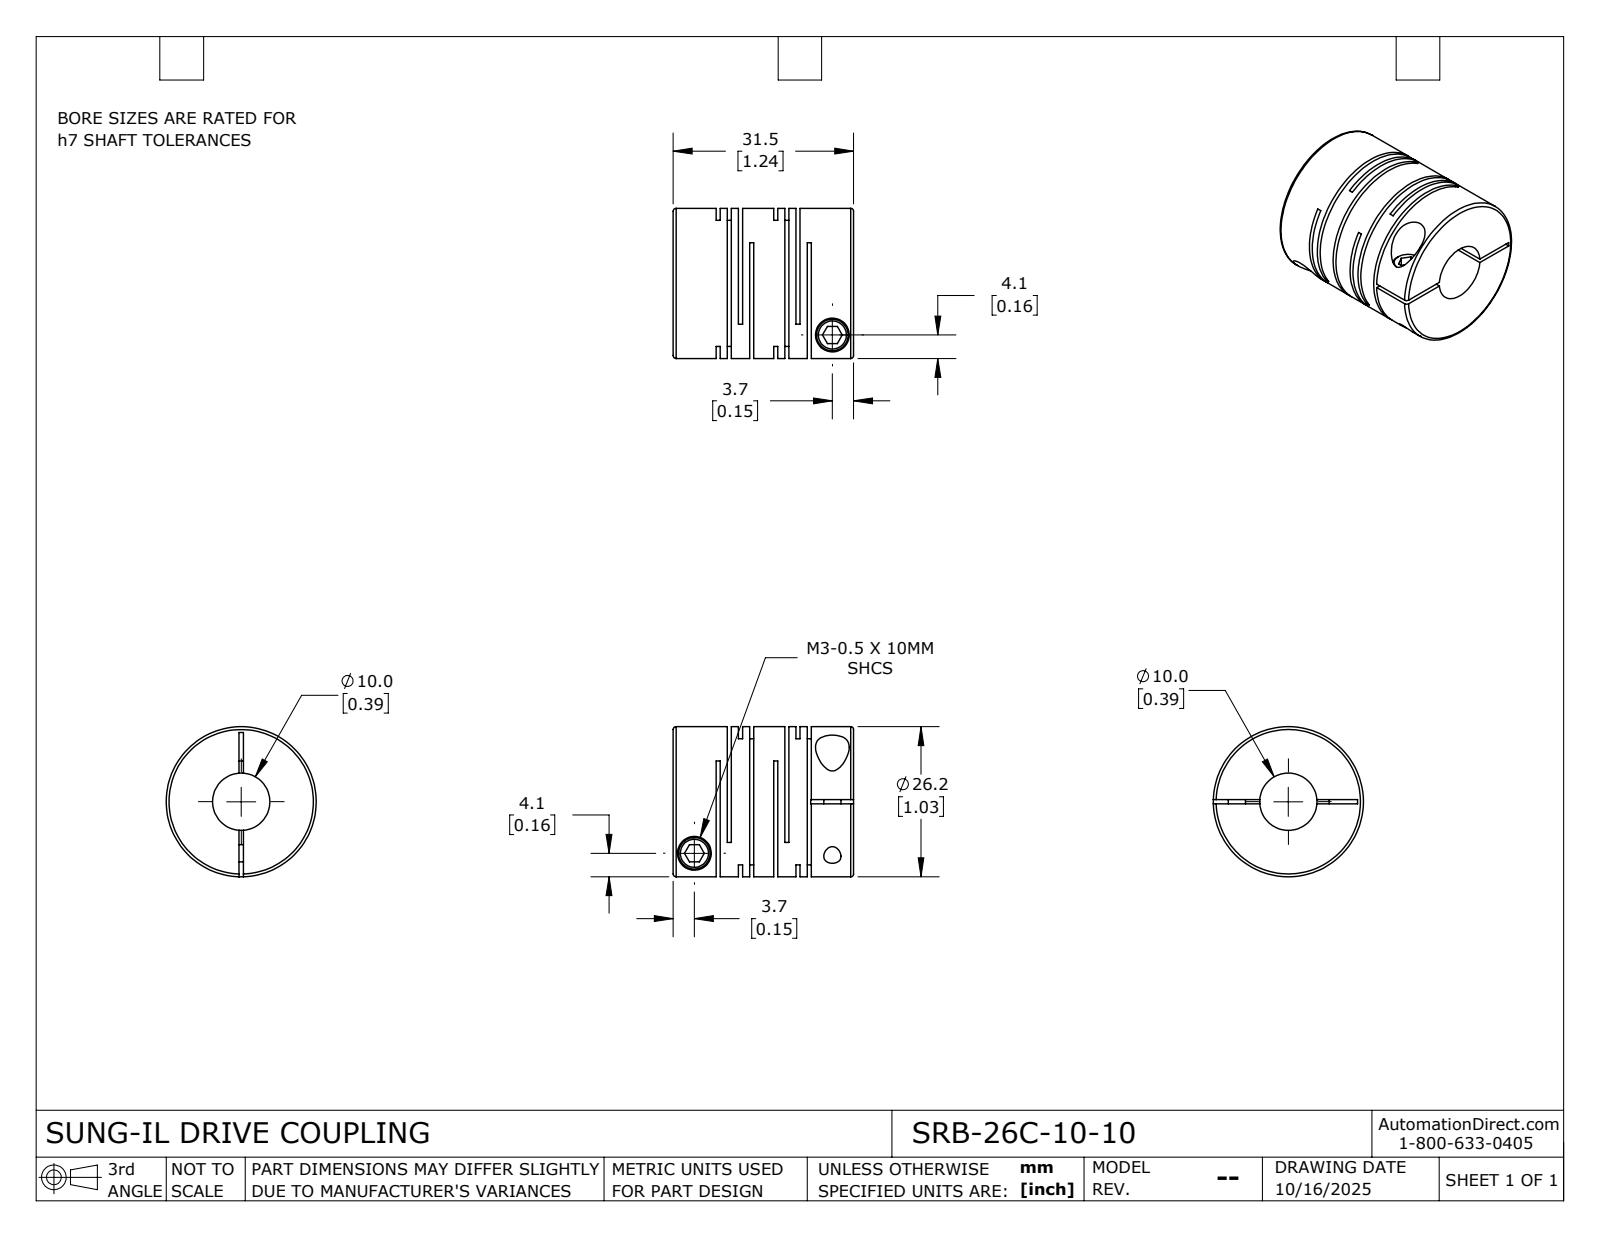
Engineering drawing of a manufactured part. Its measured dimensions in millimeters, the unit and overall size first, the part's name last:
Units: millimetres
Overall size (bounding box): 31.5 × 26.2 × 26.2
Round holes (diameter × count): ⌀3 ×2, ⌀5.9 ×2, ⌀10 ×1
Round bosses / shafts (diameter × count): ⌀5.5 ×2, ⌀26.2 ×1
Main face-to-face distances: 1.95, 10.05, 0.71, 3.9, 8.1, 12, 1.24, 2.66, 9.34, 13.95
Volume: 11 942 mm³ · Surface area: 10 723 mm²
Bodies: 1 solid, 115 faces (60 planar, 42 cylindrical, 13 other)
Part name (STEP PRODUCT): SRB-26C-10-10
STEP written by: SolidWorks 2024 (CONFIG_CONTROL_DESIGN)
